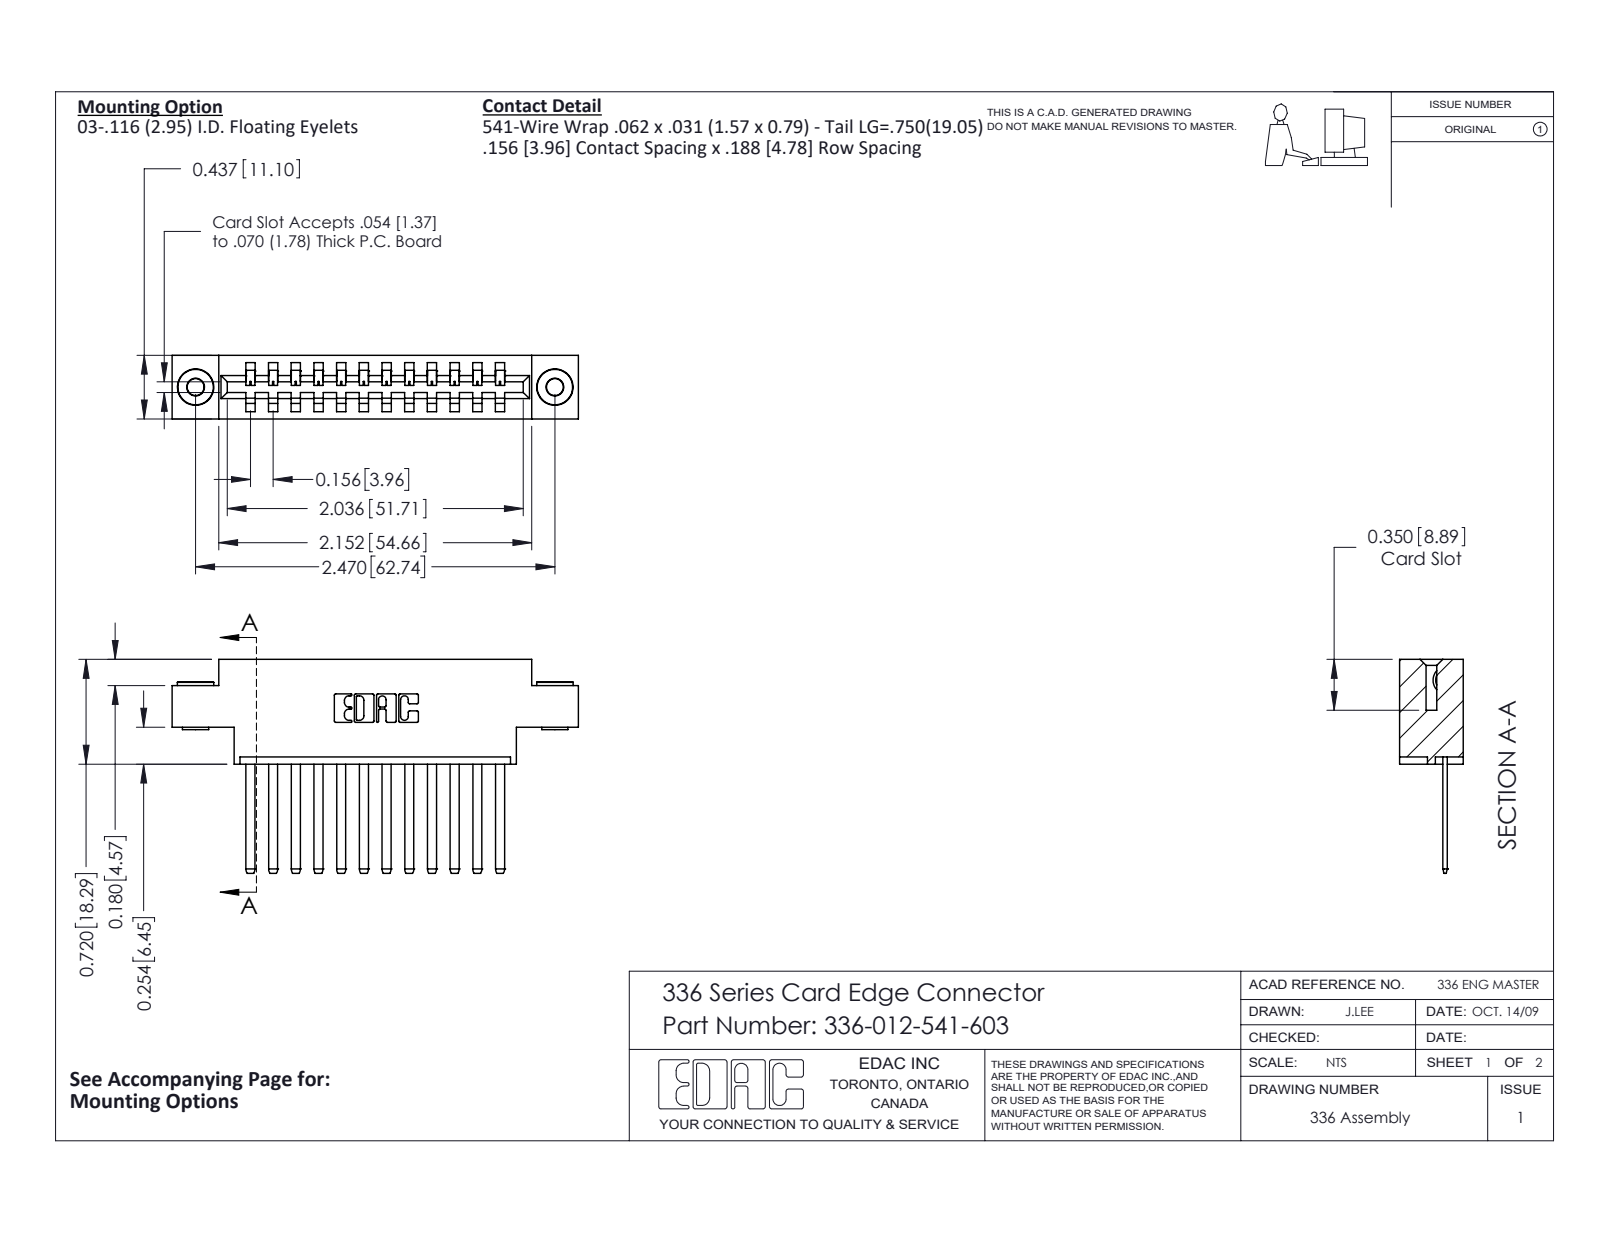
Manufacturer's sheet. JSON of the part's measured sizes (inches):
{"part_name": "336-012-541-603; 336-290-001_336-290-541; 336 Part_Offset - .156 Dia - TH; 345-250-002_345-250-002-102", "step_written_by": "SolidWorks 2020 (CONFIG_CONTROL_DESIGN)", "units": "inches", "bodies": {"solids": 15, "faces": 756, "planar": 492, "cylindrical": 256, "other": 8}, "overall_size": [2.793, 1.47, 0.437], "volume_in3": 0.579, "surface_area_in2": 15.9, "round_holes": [[0.116, 2], [0.156, 2]], "round_bosses_or_shafts": [[0.25, 2], [0.18, 2], [0.136, 2]], "partial_cylinders_radius": [[0.004, 24], [0.056, 24], [0.01, 22], [0.007, 6], [0.031, 6], [0.026, 3], [0.022, 2], [0.04, 2]], "face_to_face_distances": [0.437, 0.156, 0.624, 0.468, 0.181, 0.312, 0.312, 0.404, 0.031, 0.256], "hole_center_spacings": [2.47]}
